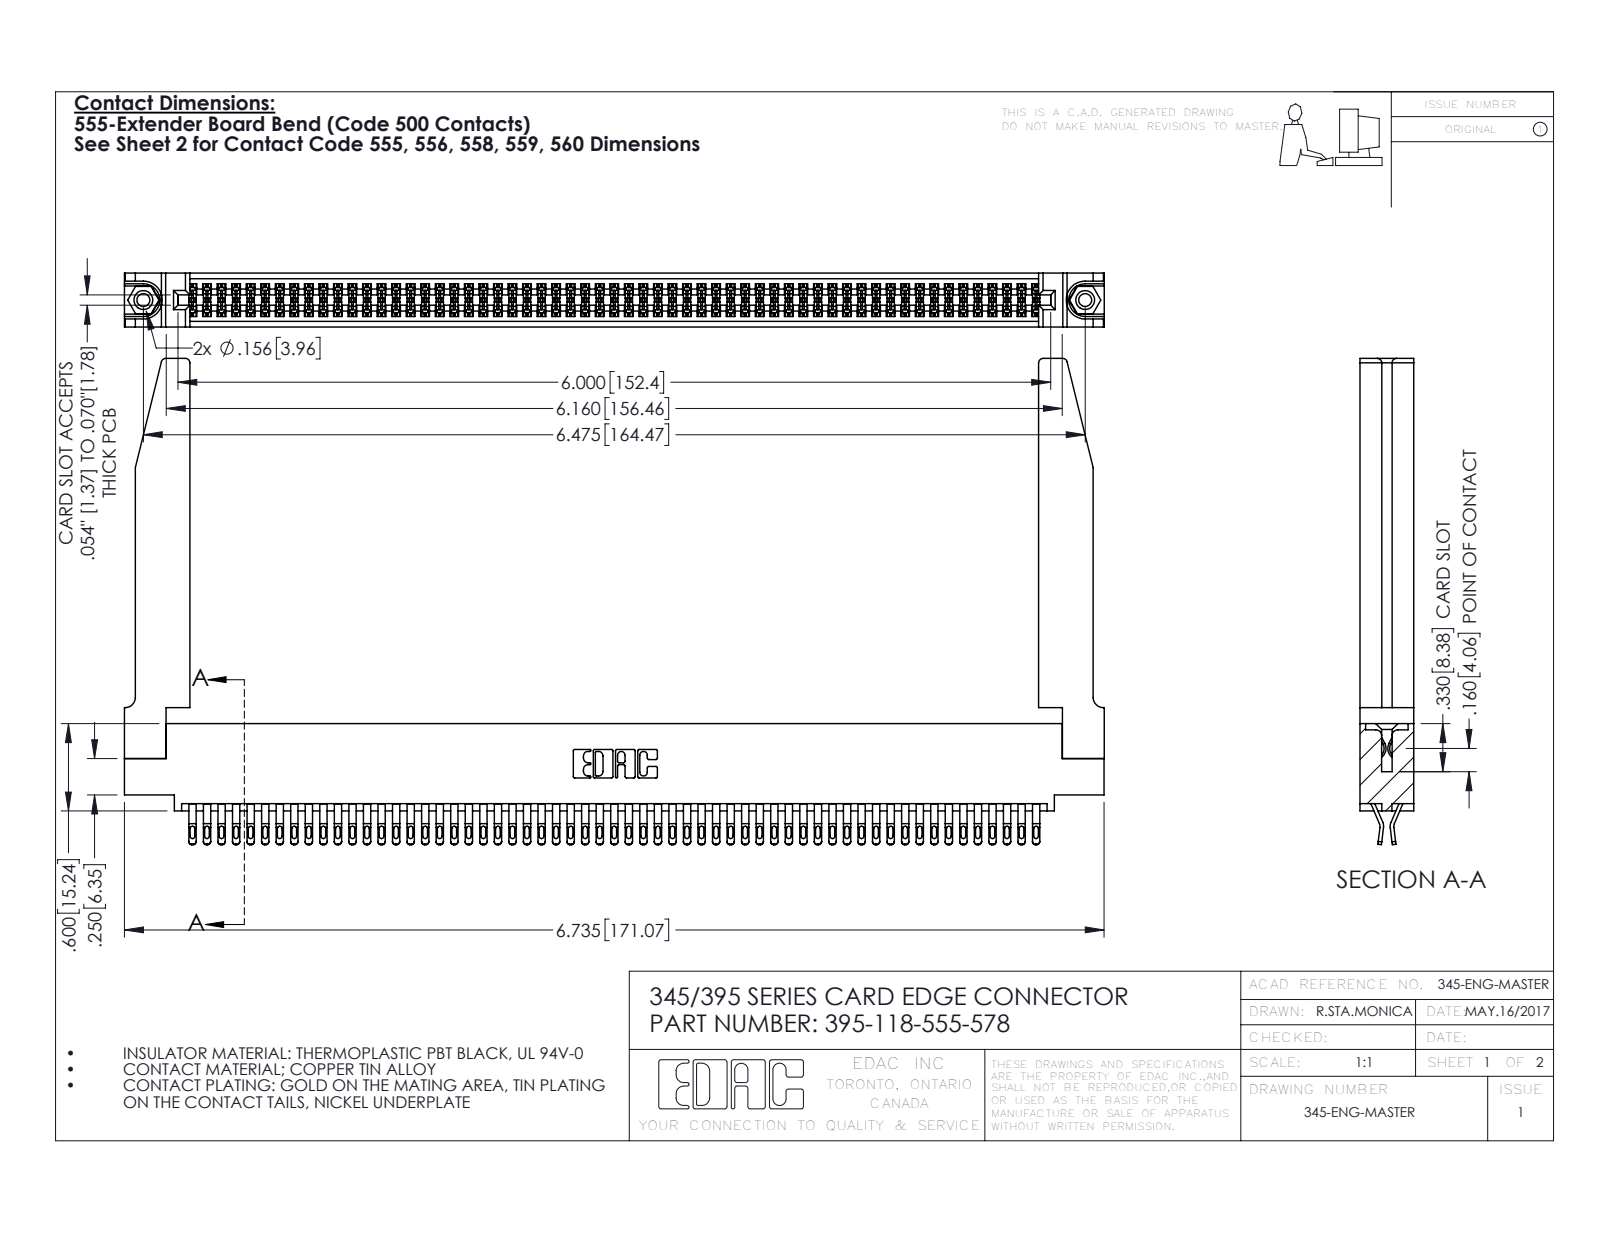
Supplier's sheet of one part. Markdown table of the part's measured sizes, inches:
| quantity | value |
| --- | --- |
| part name | 345-292-001_555 Tail; 395-118-555-578; 345-250-001_345-250-001-102; 345 Part_0.110 Offset - 0.156 Dia-TH (+1 more) |
| STEP written by | SolidWorks 2016 (CONFIG_CONTROL_DESIGN) |
| units | inches |
| bodies | 123 solids, 6972 faces (3884 planar, 3036 cylindrical, 52 other) |
| overall size | 6.736 × 3.342 × 0.37 |
| volume | 1.514 in³ |
| surface area | 52.16 in² |
| round holes (diameter × count) | 0.089 × 2, 0.125 × 2, 0.156 × 2, 0.064 × 1 |
| round bosses / shafts (diameter × count) | 0.155 × 2 |
| partial cylindrical surfaces (radius × count) | 0.016 × 295, 0.02 × 236, 0.006 × 177, 0.01 × 22, 0.03 × 8, 0.007 × 6, 0.031 × 6, 0.026 × 3 |
| main face-to-face distances | 0.072, 0.37, 0.298, 0.025, 0.098, 0.272, 0.2, 0.225, 0.175, 0.148 |
| hole center spacings | 0.27, 6.239, 6.475 |
